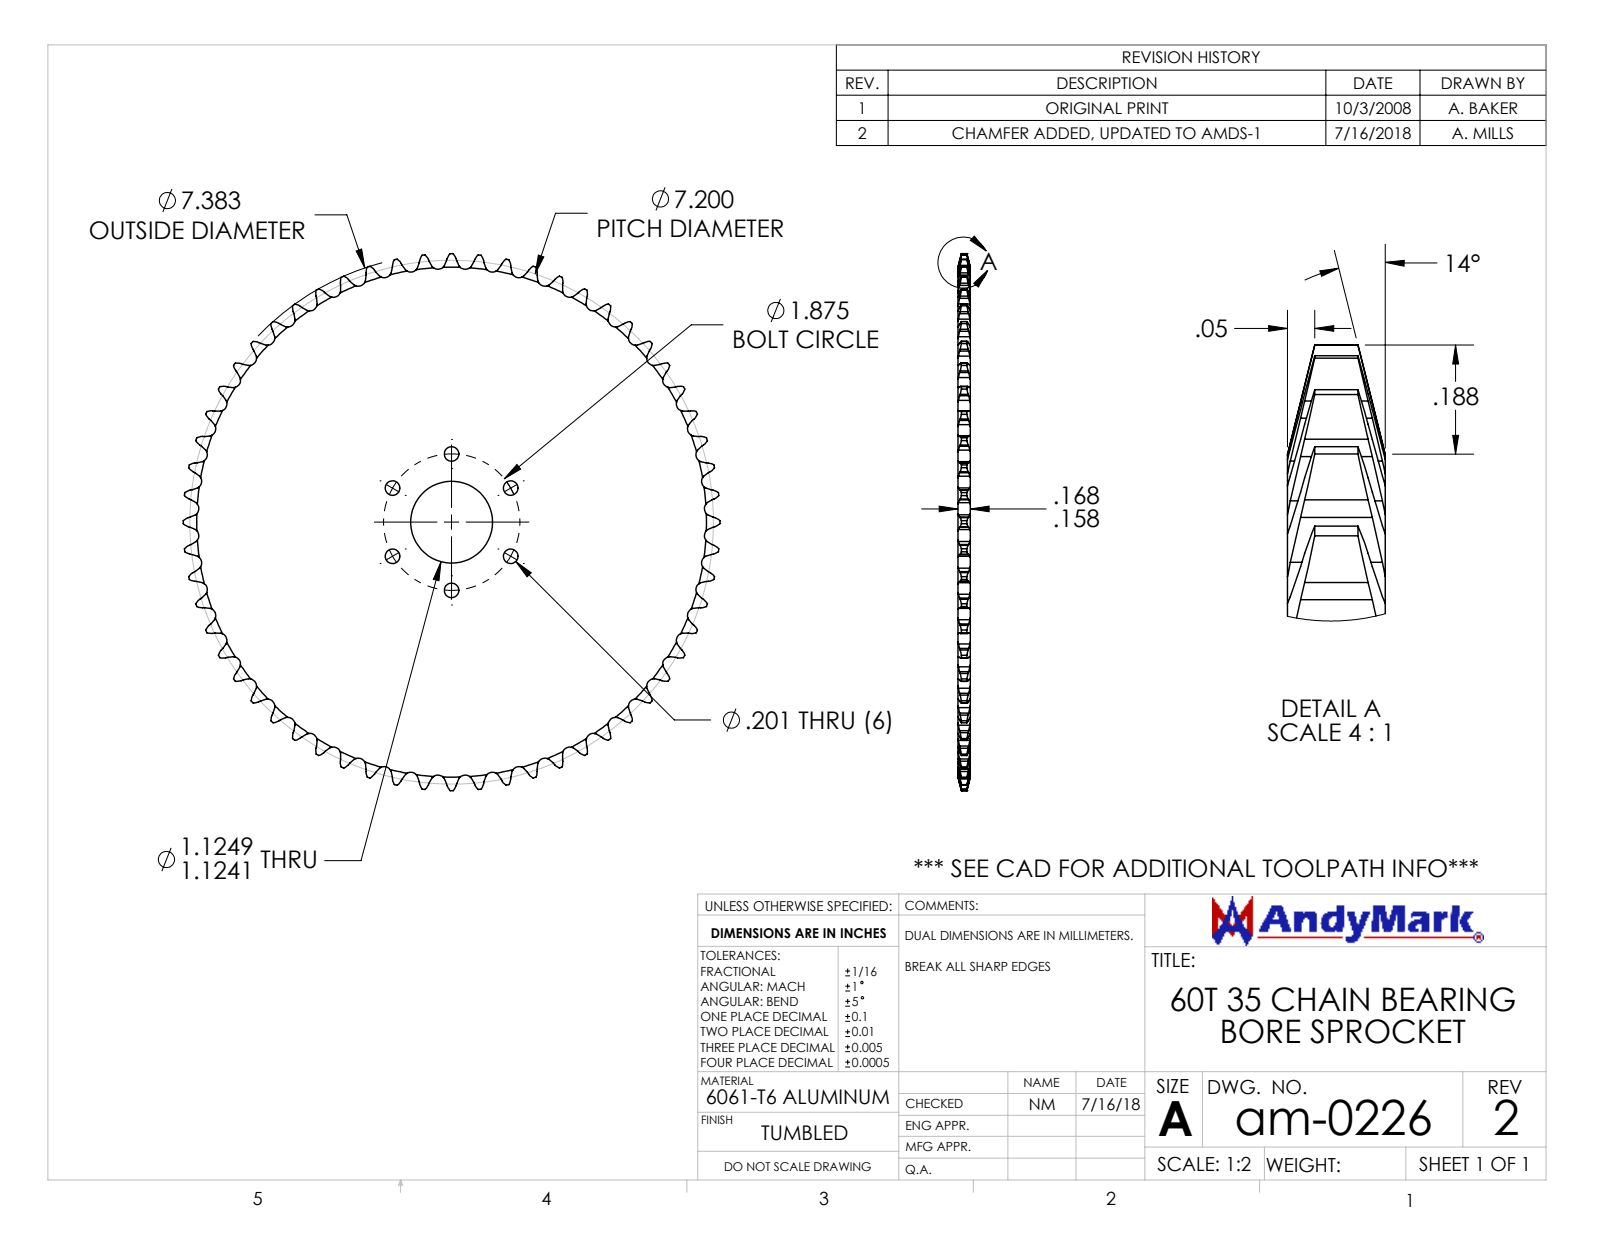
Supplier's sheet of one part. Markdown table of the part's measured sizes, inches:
| quantity | value |
| --- | --- |
| part name | am-0226_Plate Sprocket |
| STEP written by | SolidWorks 2018 (AUTOMOTIVE_DESIGN) |
| units | inches |
| bodies | 1 solid, 653 faces (122 planar, 409 cylindrical, 122 other) |
| overall size | 7.383 × 7.383 × 0.168 |
| volume | 6.464 in³ |
| surface area | 83.71 in² |
| round holes (diameter × count) | 0.201 × 6, 1.125 × 1 |
| partial cylindrical surfaces (radius × count) | 0.16 × 120, 0.262 × 120, 0.102 × 60, 3.691 × 1 |
| main face-to-face distances | 0.168, 2.11, 2.107, 2.106, 2.104, 2.112, 2.103, 2.108, 2.105, 2.109 |
| hole center spacings | 0.937, 1.624, 1.875, 0.938 |
